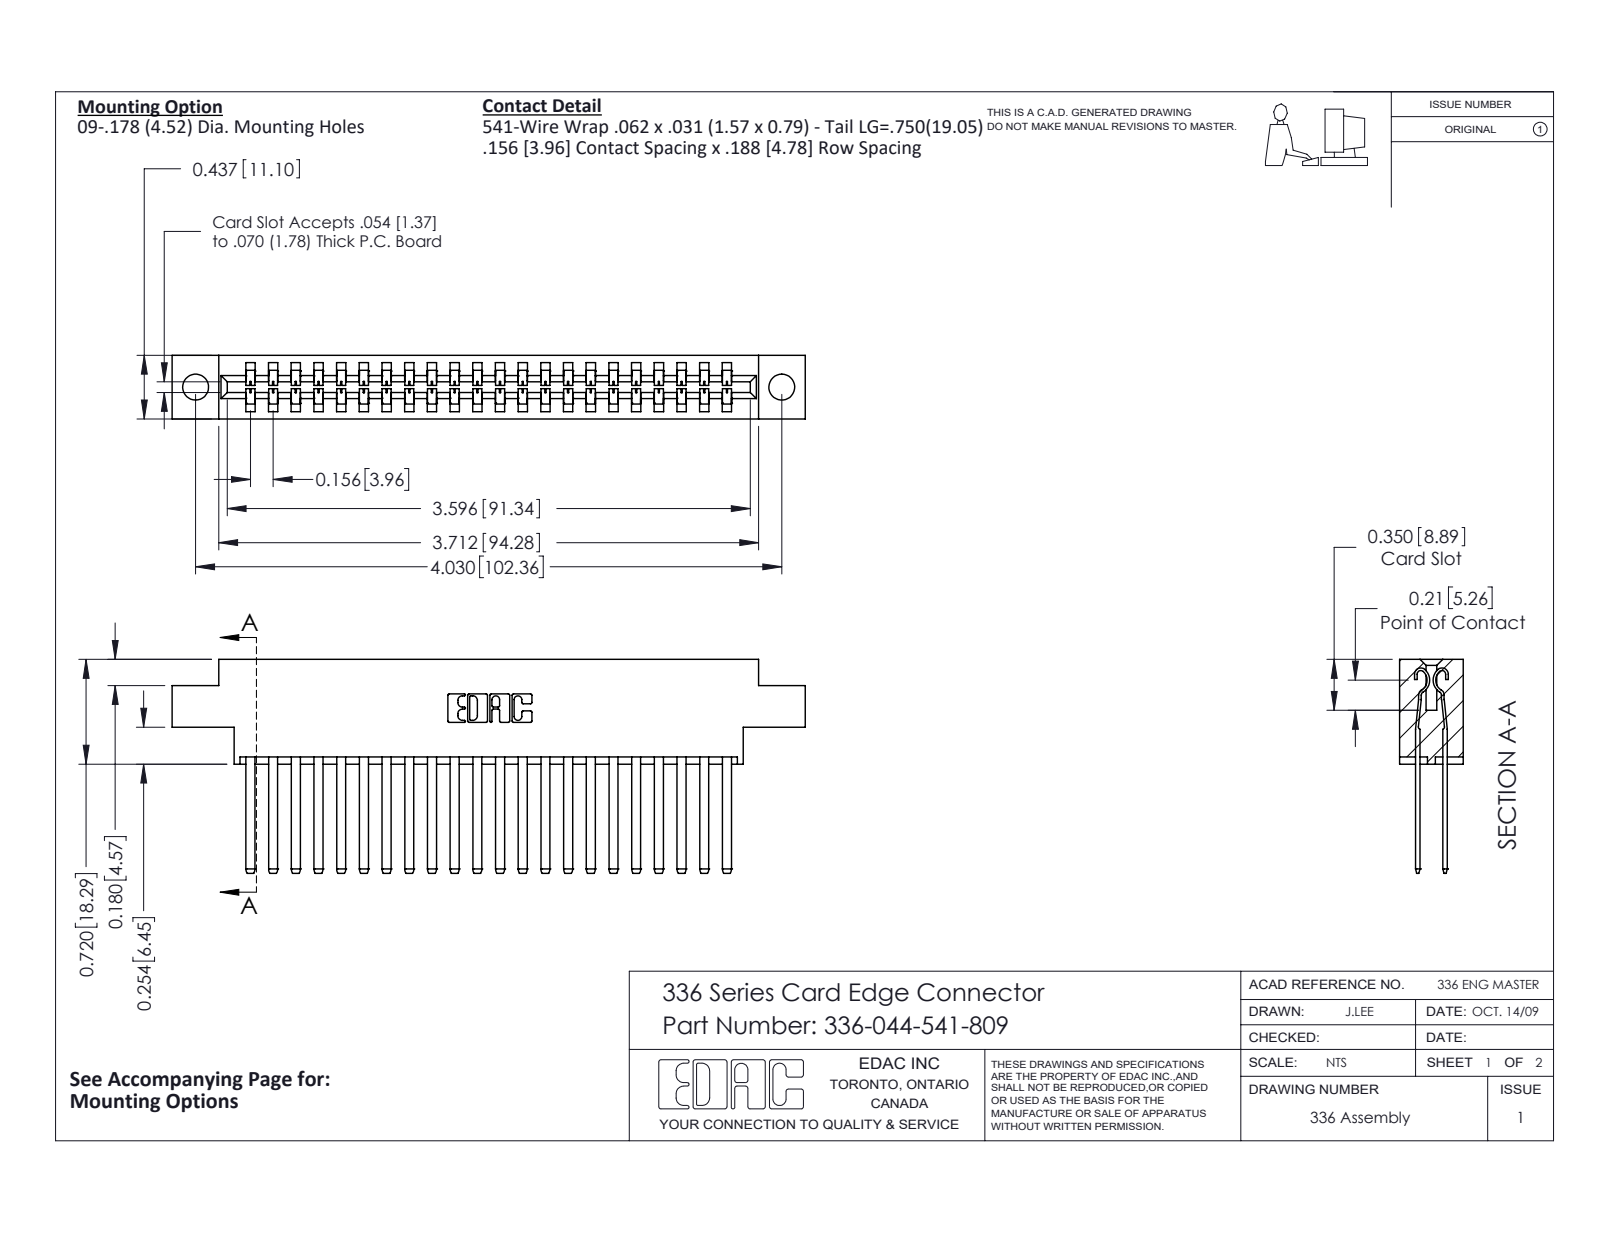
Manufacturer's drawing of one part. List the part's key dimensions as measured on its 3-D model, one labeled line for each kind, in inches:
Part name (STEP PRODUCT): 336-044-541-809; 336-290-001_336-290-541; 336 Part_Offset - .178 Dia - TH
STEP written by: SolidWorks 2020 (CONFIG_CONTROL_DESIGN)
Units: inches
Bodies: 45 solids, 1966 faces (1218 planar, 748 cylindrical, 0 other)
Overall size (bounding box): 4.353 × 1.47 × 0.437
Volume: 0.994 in³ · Surface area: 31.6 in²
Round holes (diameter × count): ⌀0.178 ×2
Partial cylindrical surfaces — rounded edges, fillets, slot ends (radius × count): R0.004 ×88, R0.056 ×44, R0.01 ×22, R0.007 ×6, R0.031 ×6, R0.022 ×4, R0.04 ×4, R0.026 ×3
Main face-to-face distances: 0.188, 0.328, 0.14, 0.297, 0.109, 0.031, 0.437, 0.033, 0.156, 0.181
Hole centre spacings: 4.03
